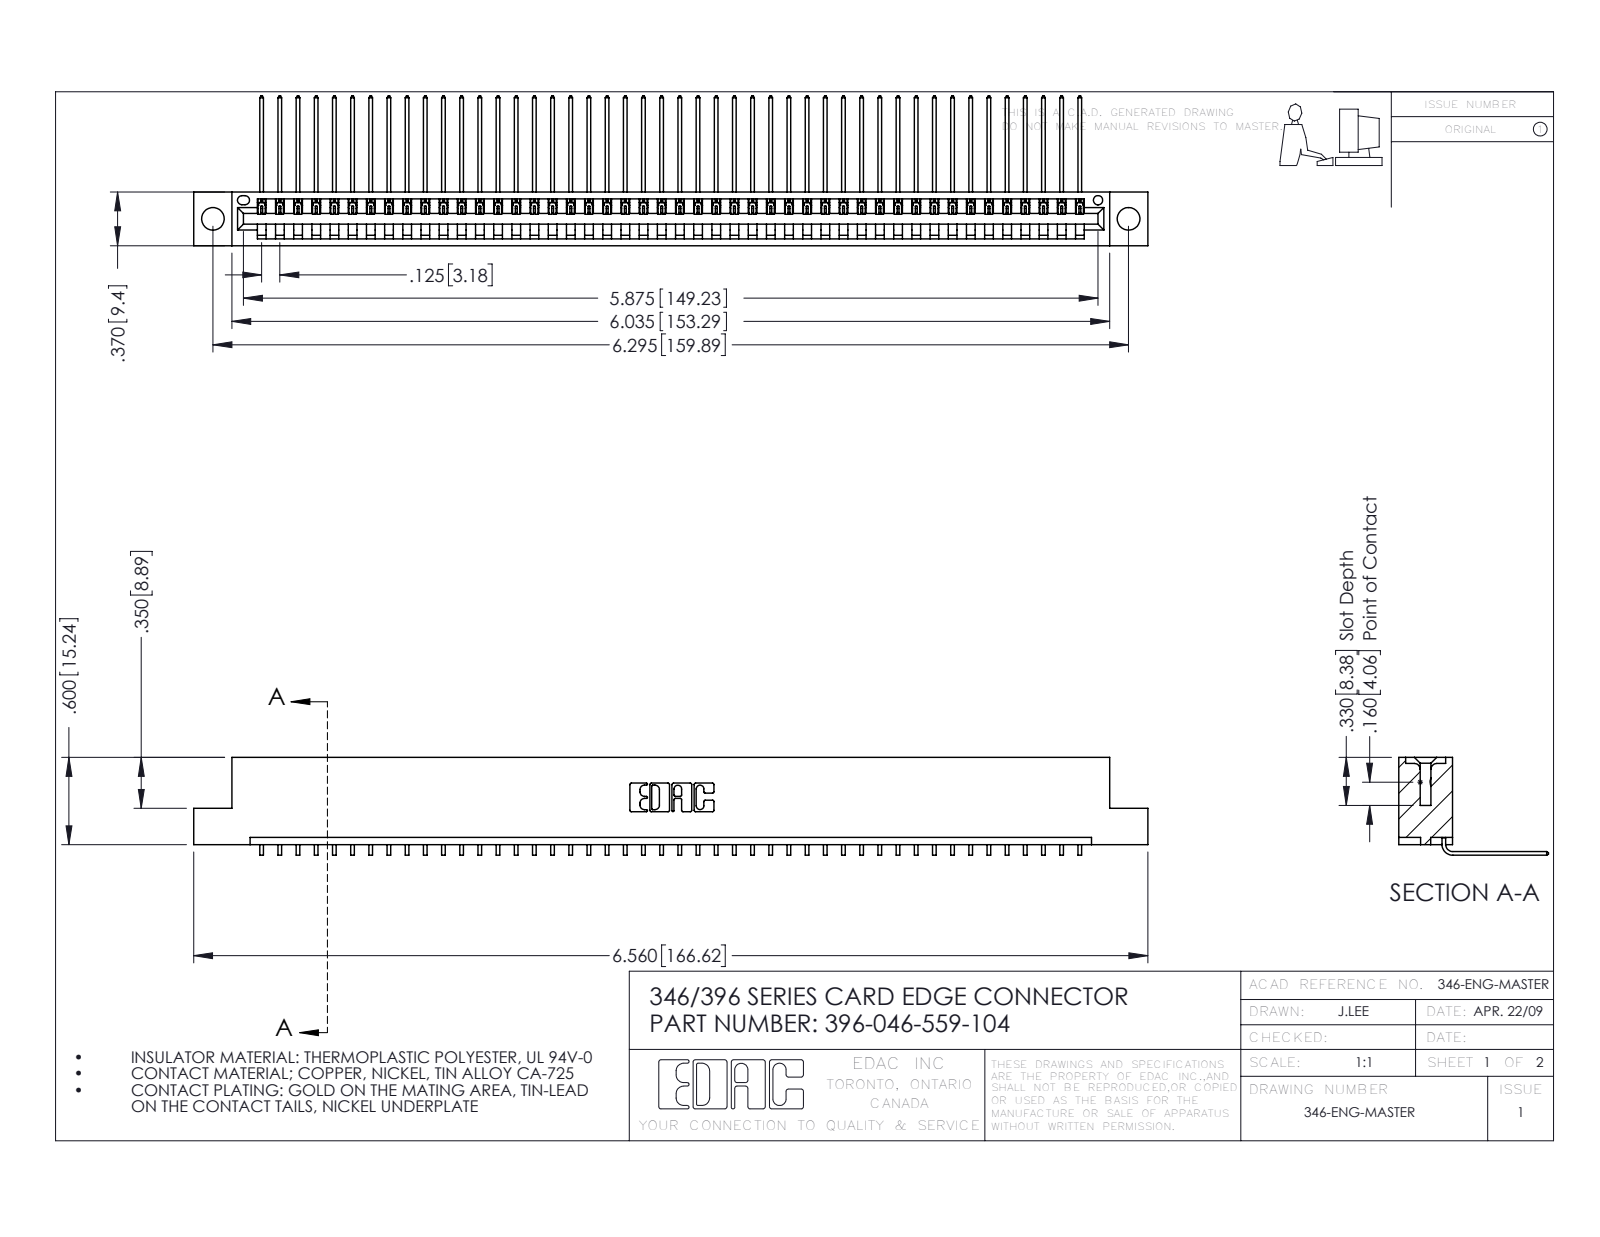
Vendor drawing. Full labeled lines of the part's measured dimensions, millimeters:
Part name (STEP PRODUCT): 396-046-559-104; 345-292-001_558 559 Tail - 1; 346 Part_Flush Mounting Lugs - 0.156 Dia-TH
STEP written by: SolidWorks 2016 (CONFIG_CONTROL_DESIGN)
Units: millimetres
Bodies: 47 solids, 2882 faces (2008 planar, 874 cylindrical, 0 other)
Overall size (bounding box): 166.6 × 26.2 × 17.1
Volume: 16 000 mm³ · Surface area: 20 810 mm²
Round holes (diameter × count): ⌀4 ×2, ⌀1.6 ×1
Partial cylindrical surfaces — rounded edges, fillets, slot ends (radius × count): R0.2 ×92, R0.3 ×22, R0.2 ×6, R0.8 ×6, R0.7 ×3, R0.8 ×2, R1 ×2, R0.4 ×1
Main face-to-face distances: 1.2, 8.2, 9.4, 0.6, 6.4, 1.8, 7.6, 3.8, 5.6, 2.5
Hole centre spacings: 6.2, 154.6, 159.9
